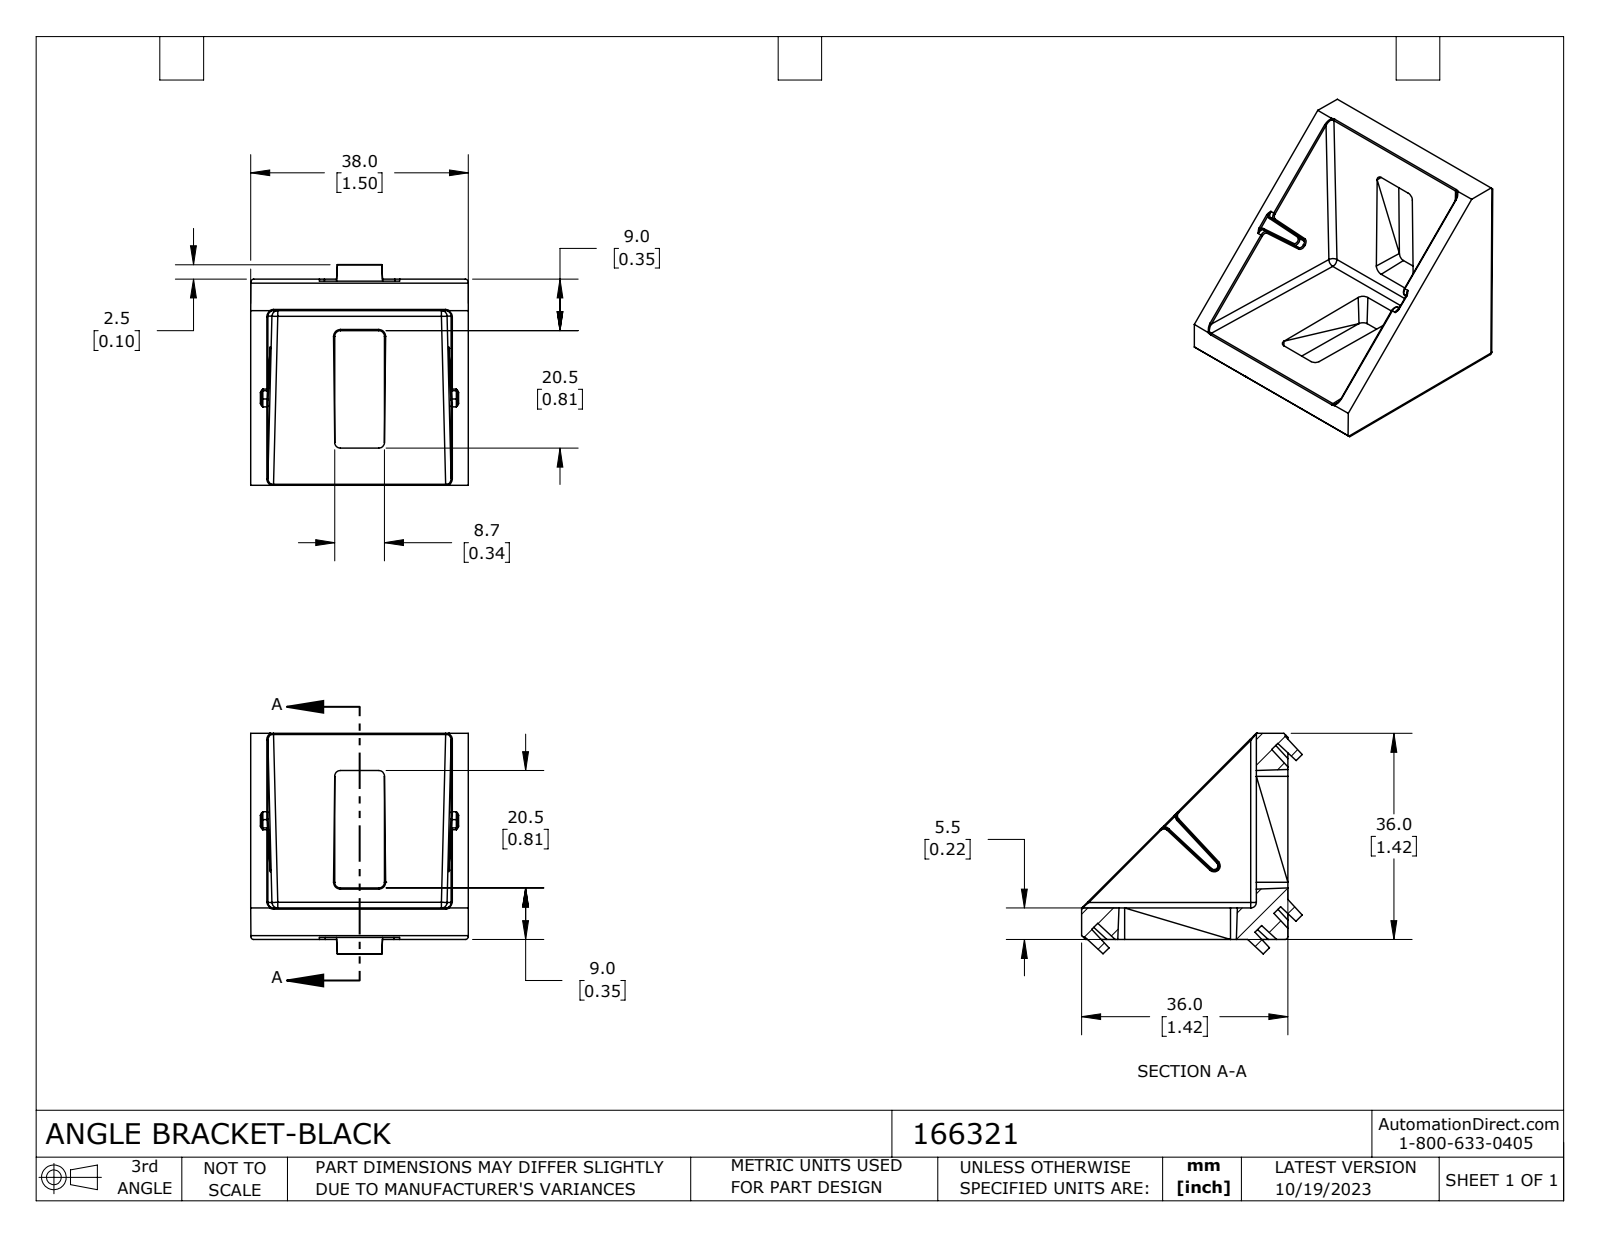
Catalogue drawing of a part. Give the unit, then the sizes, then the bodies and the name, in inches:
Units: inches
Overall size (bounding box): 1.517 × 1.517 × 1.496
Partial cylindrical surfaces — rounded edges, fillets, slot ends (radius × count): R0.012 ×66, R0.039 ×15, R0.008 ×14, R0.02 ×11, R0.034 ×1
Main face-to-face distances: 0.217, 1.201, 1.417, 1.299, 0.098, 0.118, 0.944, 0.343, 0.807, 0.757
Volume: 0.786 in³ · Surface area: 13.48 in²
Bodies: 1 solid, 387 faces (110 planar, 149 cylindrical, 128 other)
Part name (STEP PRODUCT): 166321
STEP written by: SolidWorks 2023 (CONFIG_CONTROL_DESIGN)
